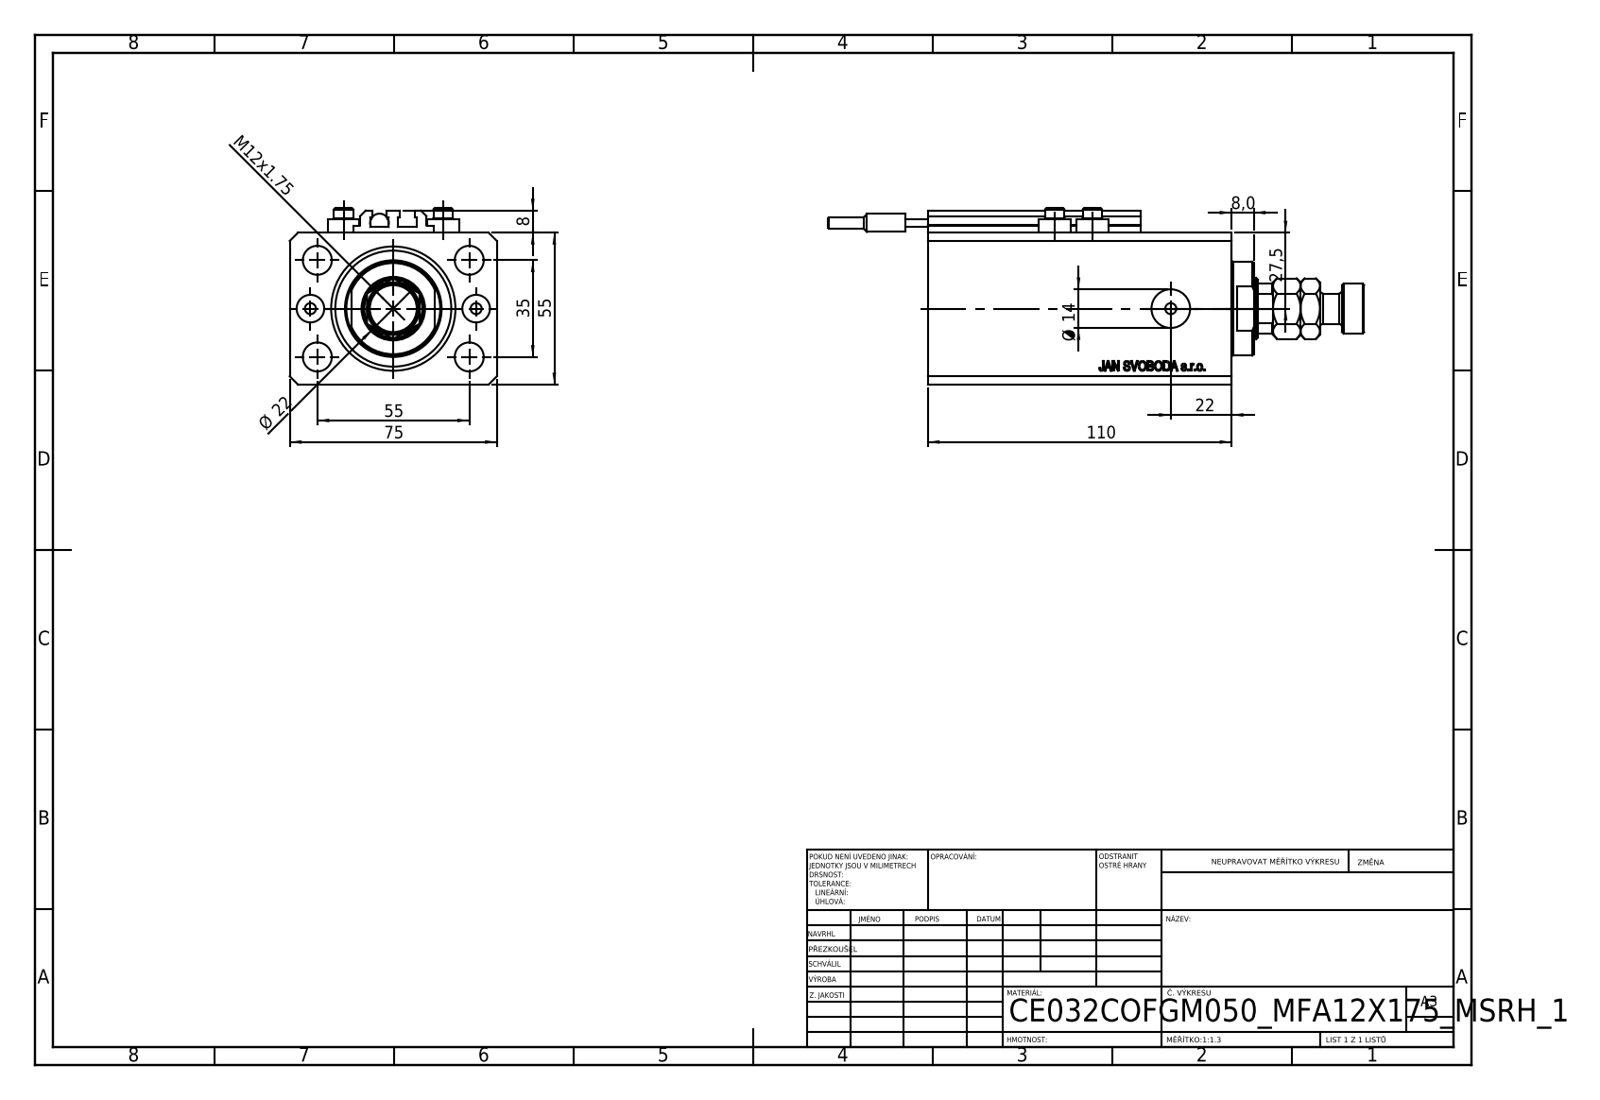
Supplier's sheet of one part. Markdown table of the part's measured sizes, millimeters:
| quantity | value |
| --- | --- |
| part name | ALLEN BOLT V250CE; V250CE_VC_C; SWITCH_V250CE; V250CE_C_Body (+2 more) |
| STEP written by | SolidWorks 2019 (CONFIG_CONTROL_DESIGN) |
| units | millimeters |
| bodies | 10 solids, 1112 faces (536 planar, 96 cylindrical, 480 other) |
| overall size | 194 × 75 × 64 |
| volume | 418 785 mm³ |
| surface area | 95 189 mm² |
| round holes (diameter × count) | 4 × 8, 10.5 × 5, 10 × 2, 14 × 2, 22 × 1, 32 × 1, 45 × 1 |
| round bosses / shafts (diameter × count) | 11.6 × 4, 7 × 4, 34 × 1, 18 × 1, 11 × 1, 6.8 × 1, 6.5 × 1, 4 × 1 |
| partial cylindrical surfaces (radius × count) | 0.2 × 10, 10.5 × 1 |
| main face-to-face distances | 55, 75, 15, 110, 95, 9.9, 85.1, 100.1, 2.5, 3 |
| hole center spacings | 17.68, 32.6, 60.1, 13.6, 30, 35, 36, 38.48 |
